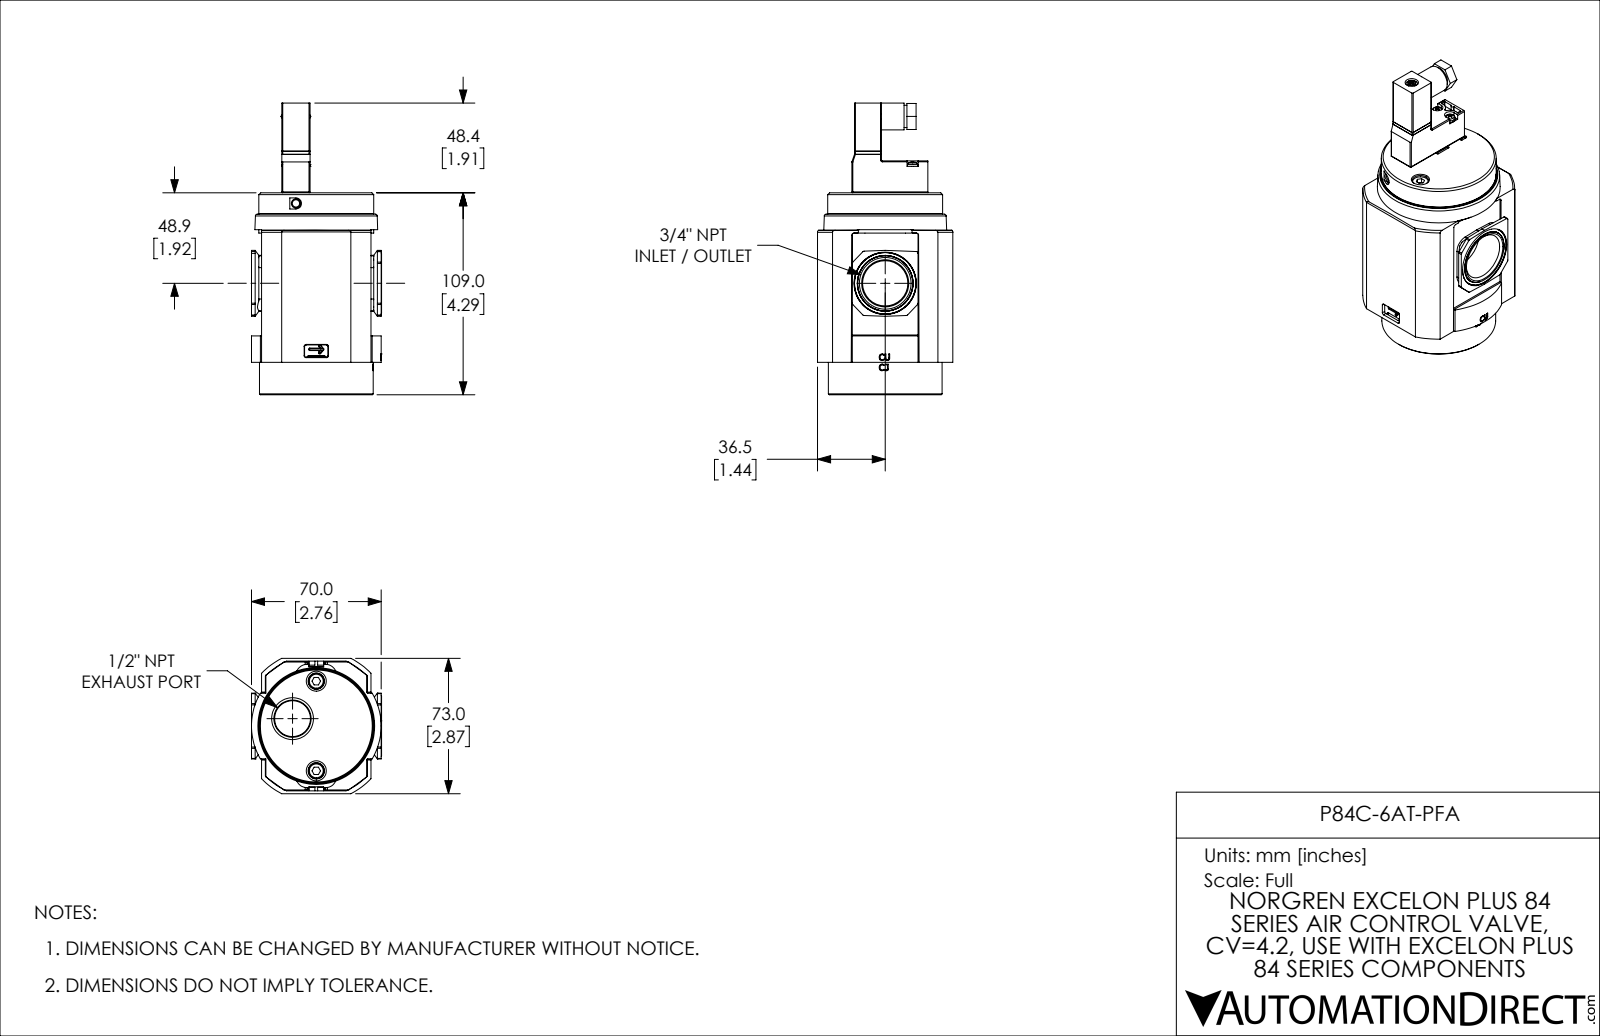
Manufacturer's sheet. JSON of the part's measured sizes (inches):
{"part_name": "P84C-6AT-PFA", "step_written_by": "SolidWorks 2021 (CONFIG_CONTROL_DESIGN)", "units": "inches", "bodies": {"solids": 7, "faces": 843, "planar": 396, "cylindrical": 250, "other": 197}, "overall_size": [6.195, 2.874, 2.766], "volume_in3": 25.25, "surface_area_in2": 149.4, "round_holes": [[0.194, 4], [0.209, 4], [0.346, 4], [0.059, 3], [0.097, 3], [0.031, 2], [0.122, 2], [0.335, 2], [0.15, 1], [0.268, 1], [0.283, 1]], "round_bosses_or_shafts": [[0.335, 4], [0.197, 4], [0.118, 2], [2.441, 1], [2.417, 1], [2.323, 1], [0.571, 1], [0.472, 1]], "partial_cylinders_radius": [[0.02, 25], [0.01, 14], [0.039, 13], [0.118, 4], [0.236, 4], [0.248, 4], [0.022, 2], [0.037, 2]], "face_to_face_distances": [0.059, 2.764, 0.079, 2.795, 2.815, 2.736, 0.02, 0.443, 2.756, 3.207], "hole_center_spacings": [0.15, 0.199, 0.213, 0.28, 0.489, 0.98, 1.841, 0.056]}
